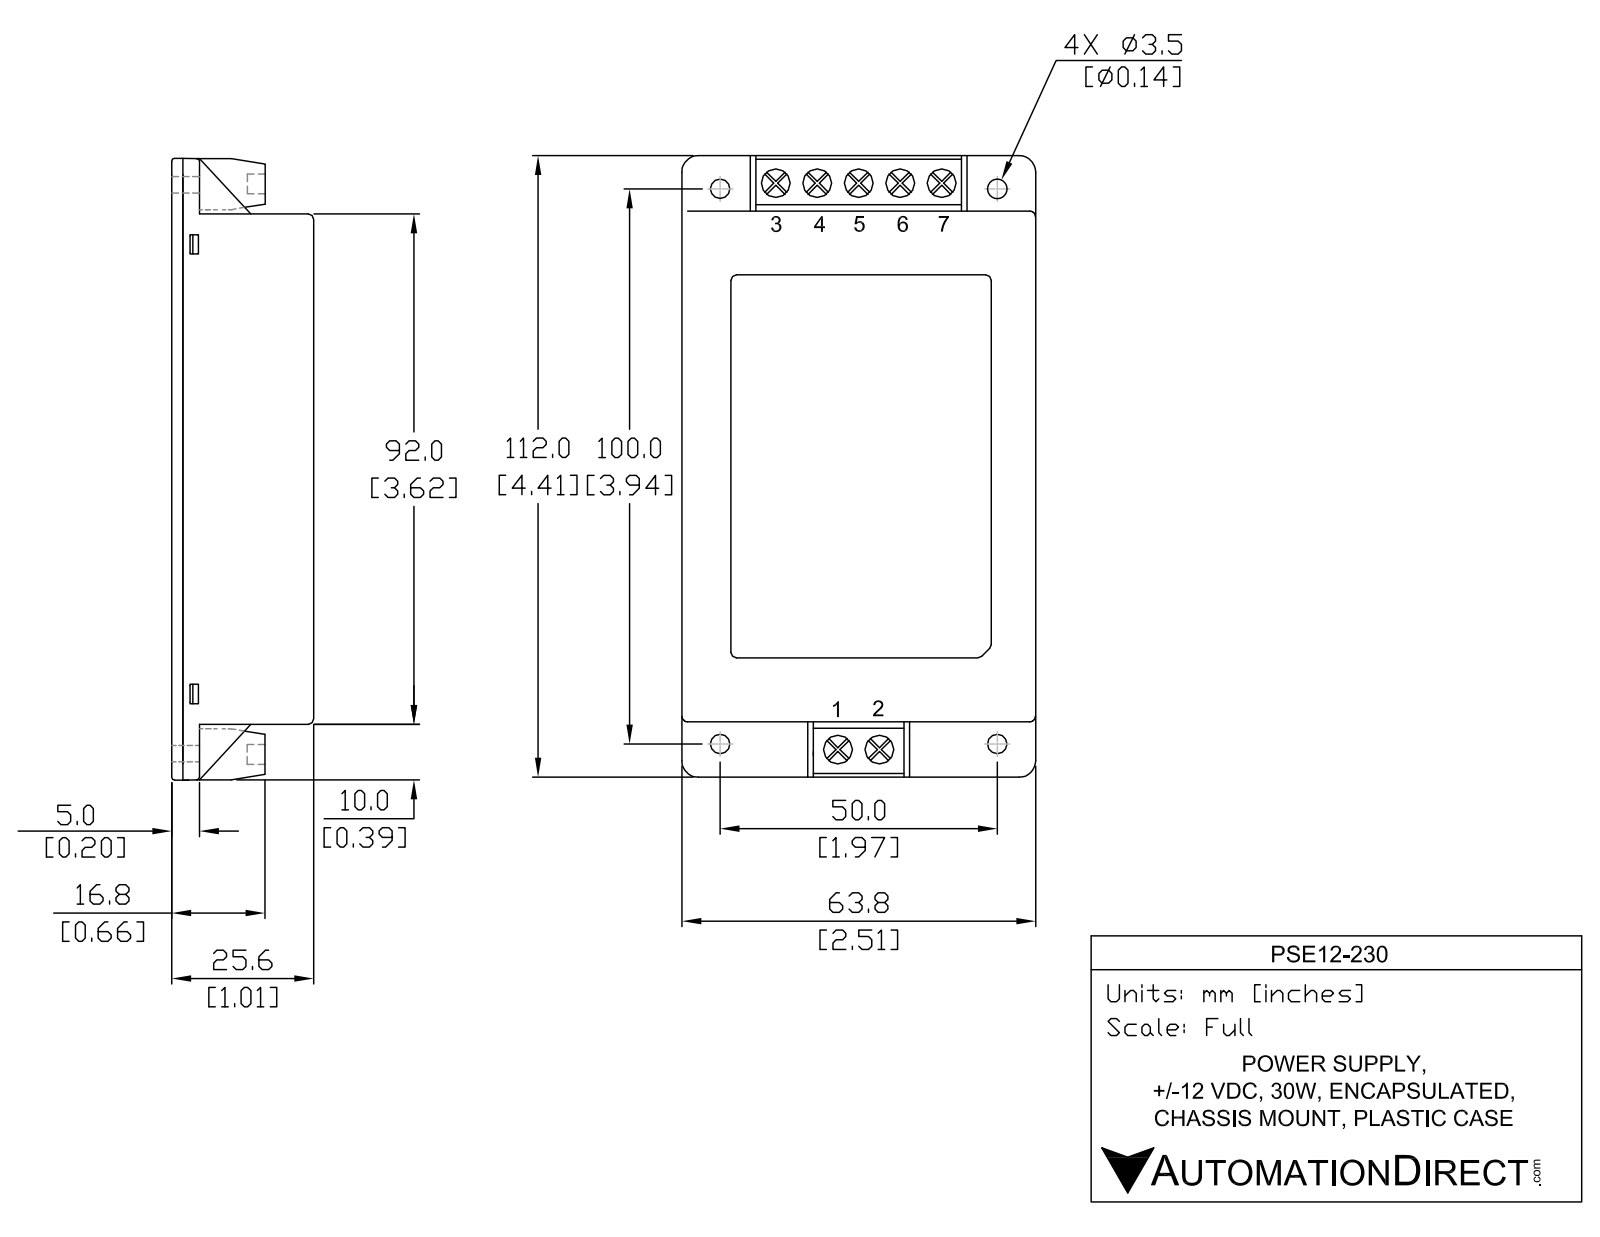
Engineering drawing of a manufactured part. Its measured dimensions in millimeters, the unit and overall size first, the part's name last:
Units: millimetres
Overall size (bounding box): 112 × 63.8 × 25.7
Round holes (diameter × count): ⌀5.1 ×7, ⌀3.6 ×4
Partial cylindrical surfaces — rounded edges, fillets, slot ends (radius × count): R0.8 ×20, R3.2 ×4
Main face-to-face distances: 2, 2, 23.6, 25.6, 23.6, 25.7, 23.7, 63.8, 91.9, 0.4
Hole centre spacings: 6.6, 13.2, 6.6, 21.7, 28.3, 50, 100.1, 102
Volume: 161 200 mm³ · Surface area: 39 030 mm²
Bodies: 2 solids, 374 faces (246 planar, 62 cylindrical, 66 other)
Part name (STEP PRODUCT): PSE12-230
STEP written by: SolidWorks 2011 (CONFIG_CONTROL_DESIGN)
